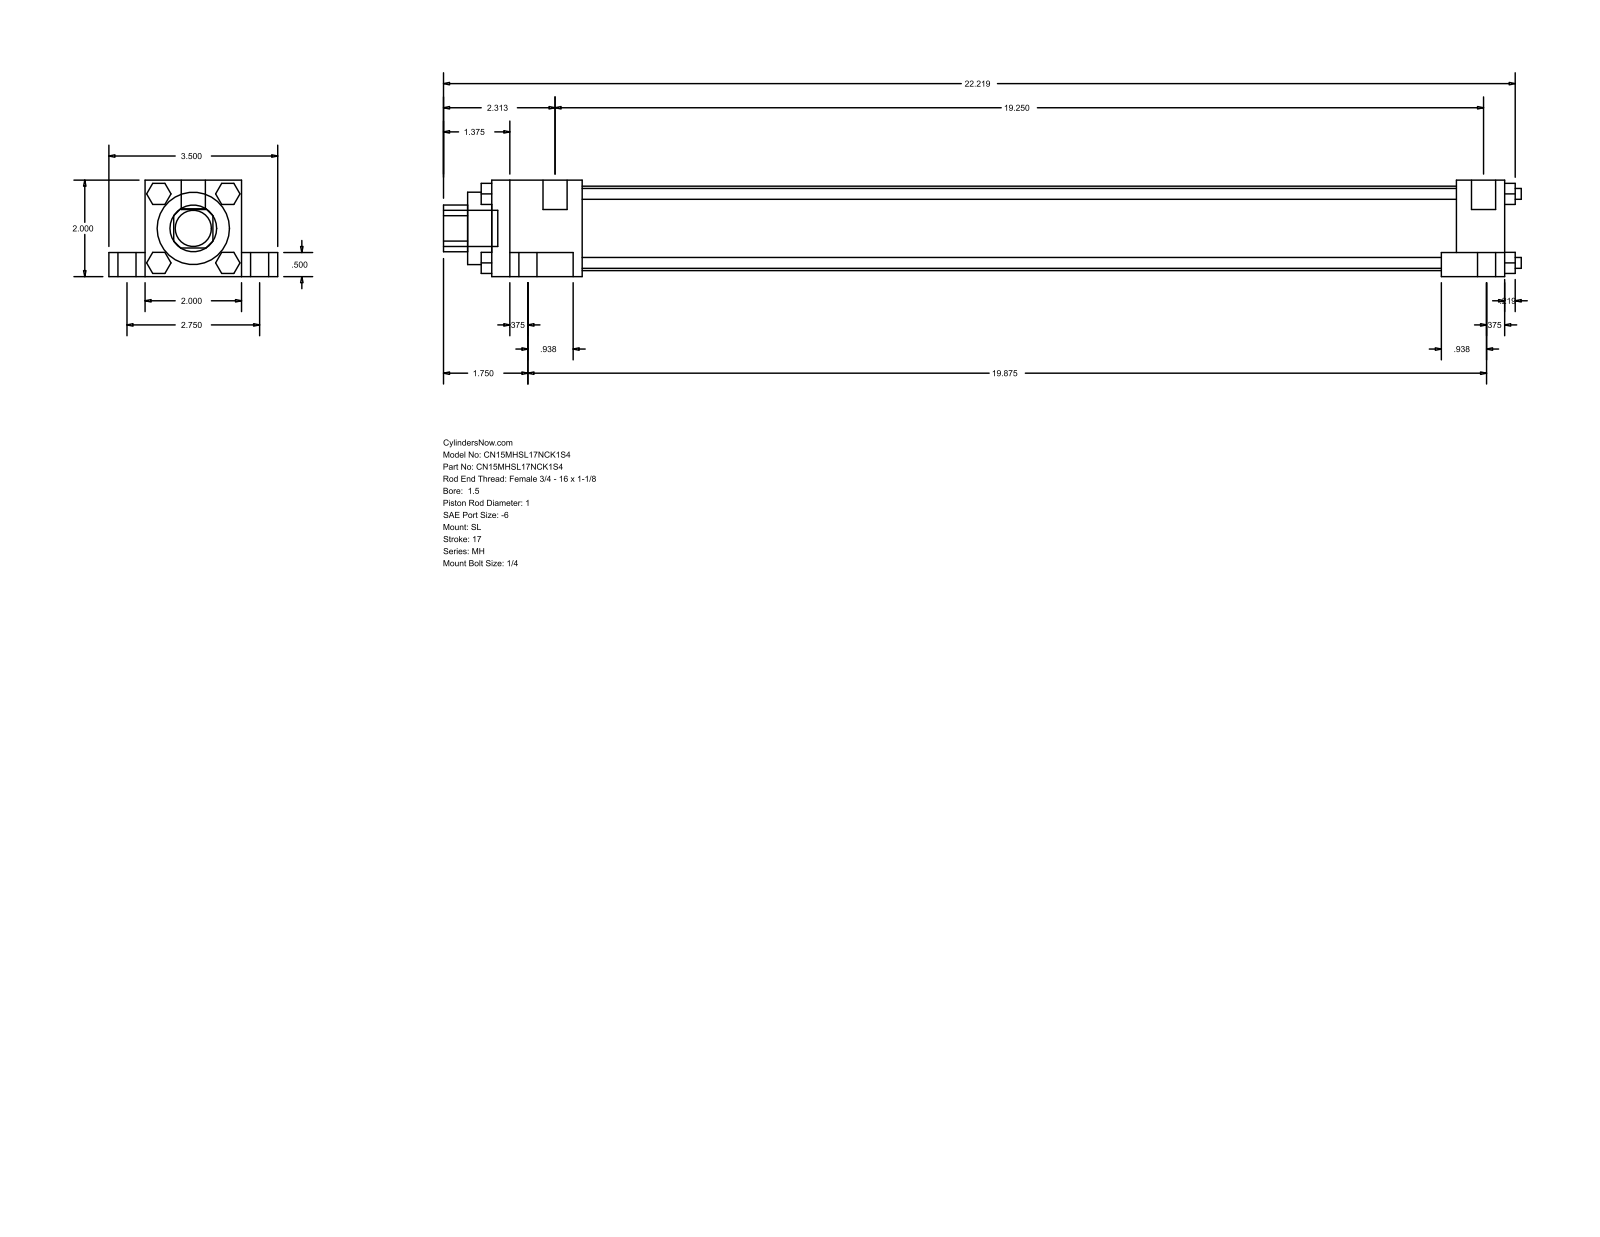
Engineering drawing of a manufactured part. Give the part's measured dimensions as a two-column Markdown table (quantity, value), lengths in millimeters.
| quantity | value |
| --- | --- |
| part name | MH_SL__0150_1 |
| STEP written by | GSSL Pune (CONFIG_CONTROL_DESIGN) |
| units | millimeters |
| bodies | 0 solids, 148 faces (112 planar, 36 cylindrical, 0 other) |
| overall size | 567.53 × 88.9 × 50.8 |
| round holes (diameter × count) | 25.4 × 1, 38.1 × 1, 44.45 × 1 |
| round bosses / shafts (diameter × count) | 15.88 × 4, 9.53 × 4, 5.71 × 4, 5.56 × 4, 12.7 × 2, 19.05 × 1 |
| partial cylindrical surfaces (radius × count) | 12.29 × 1 |
| main face-to-face distances | 50.8, 12.7, 38.1, 19.05, 69.85, 533.4, 25.4, 9.52, 33.34, 490.54 |
